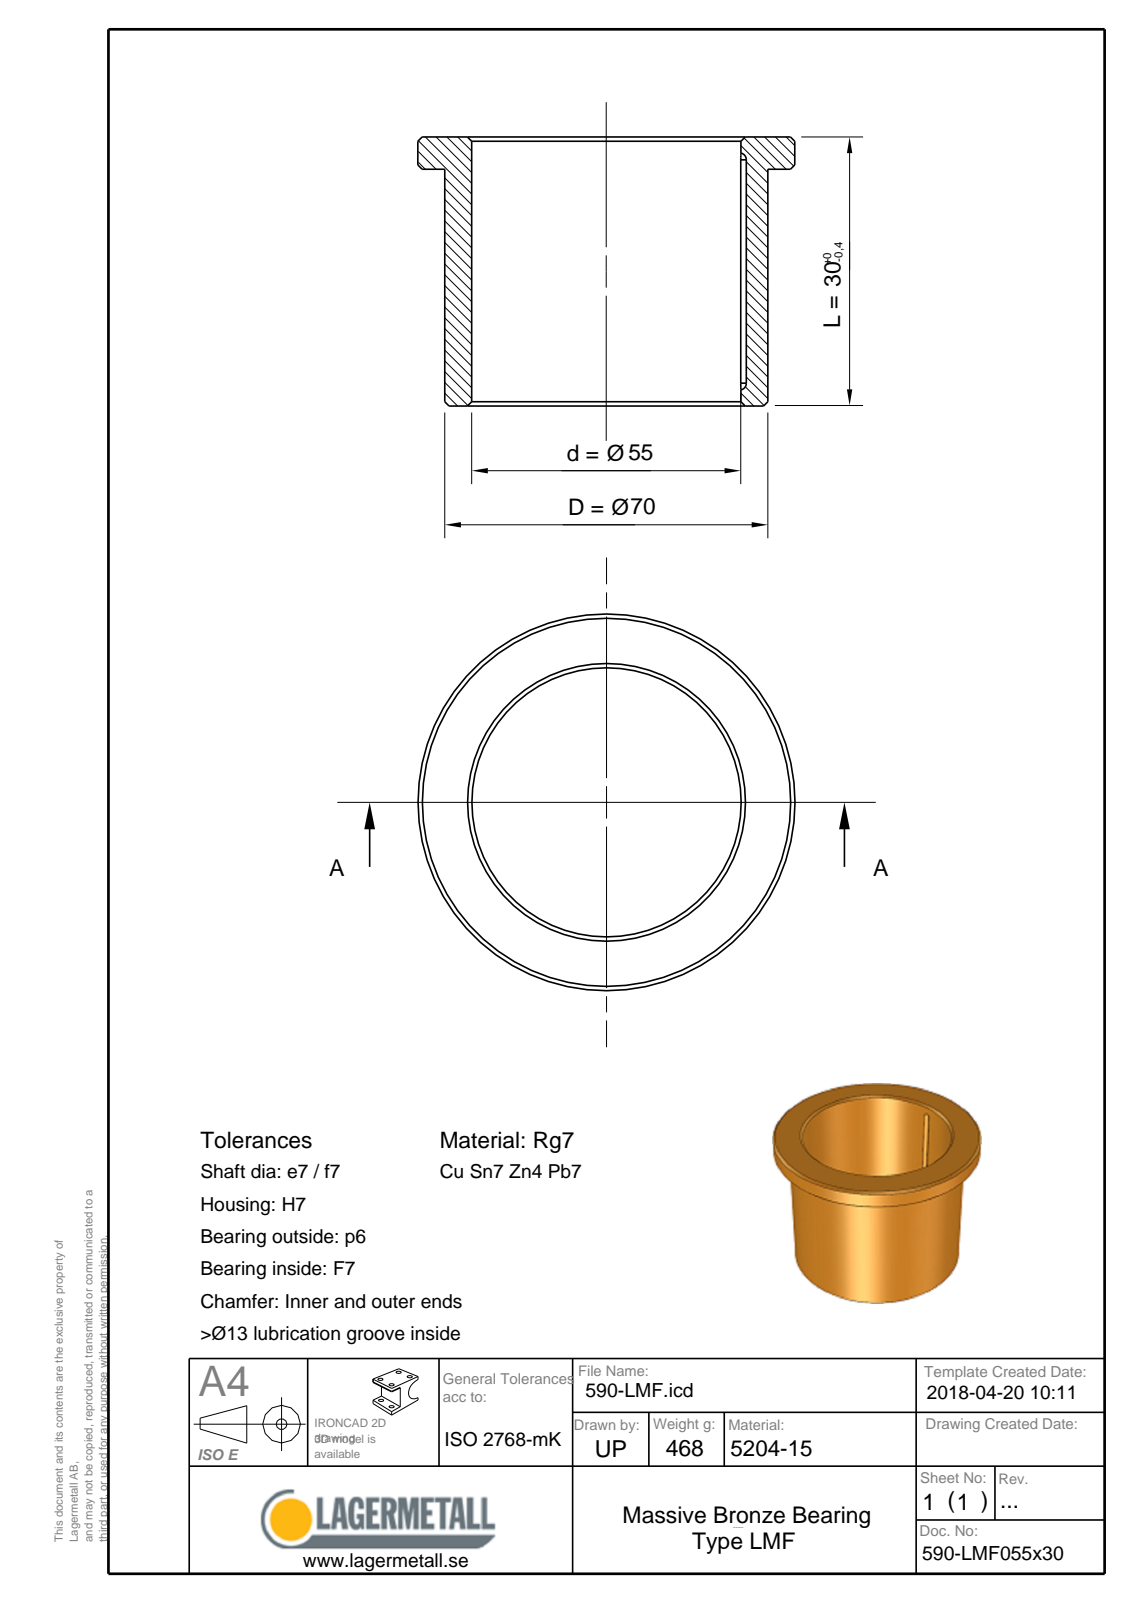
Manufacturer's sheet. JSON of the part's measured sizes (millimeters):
{"part_name": "590-LMF055x30", "step_written_by": "Spatial InterOp 3D (CONFIG_CONTROL_DESIGN)", "units": "millimeters", "bodies": {"solids": 1, "faces": 16, "planar": 4, "cylindrical": 5, "other": 7}, "overall_size": [80, 80, 30], "volume_mm3": 53218, "surface_area_mm2": 16858, "round_holes": [[55, 1]], "round_bosses_or_shafts": [[80, 1], [70, 1]], "partial_cylinders_radius": [[1.25, 2]], "face_to_face_distances": [30, 22, 8]}
